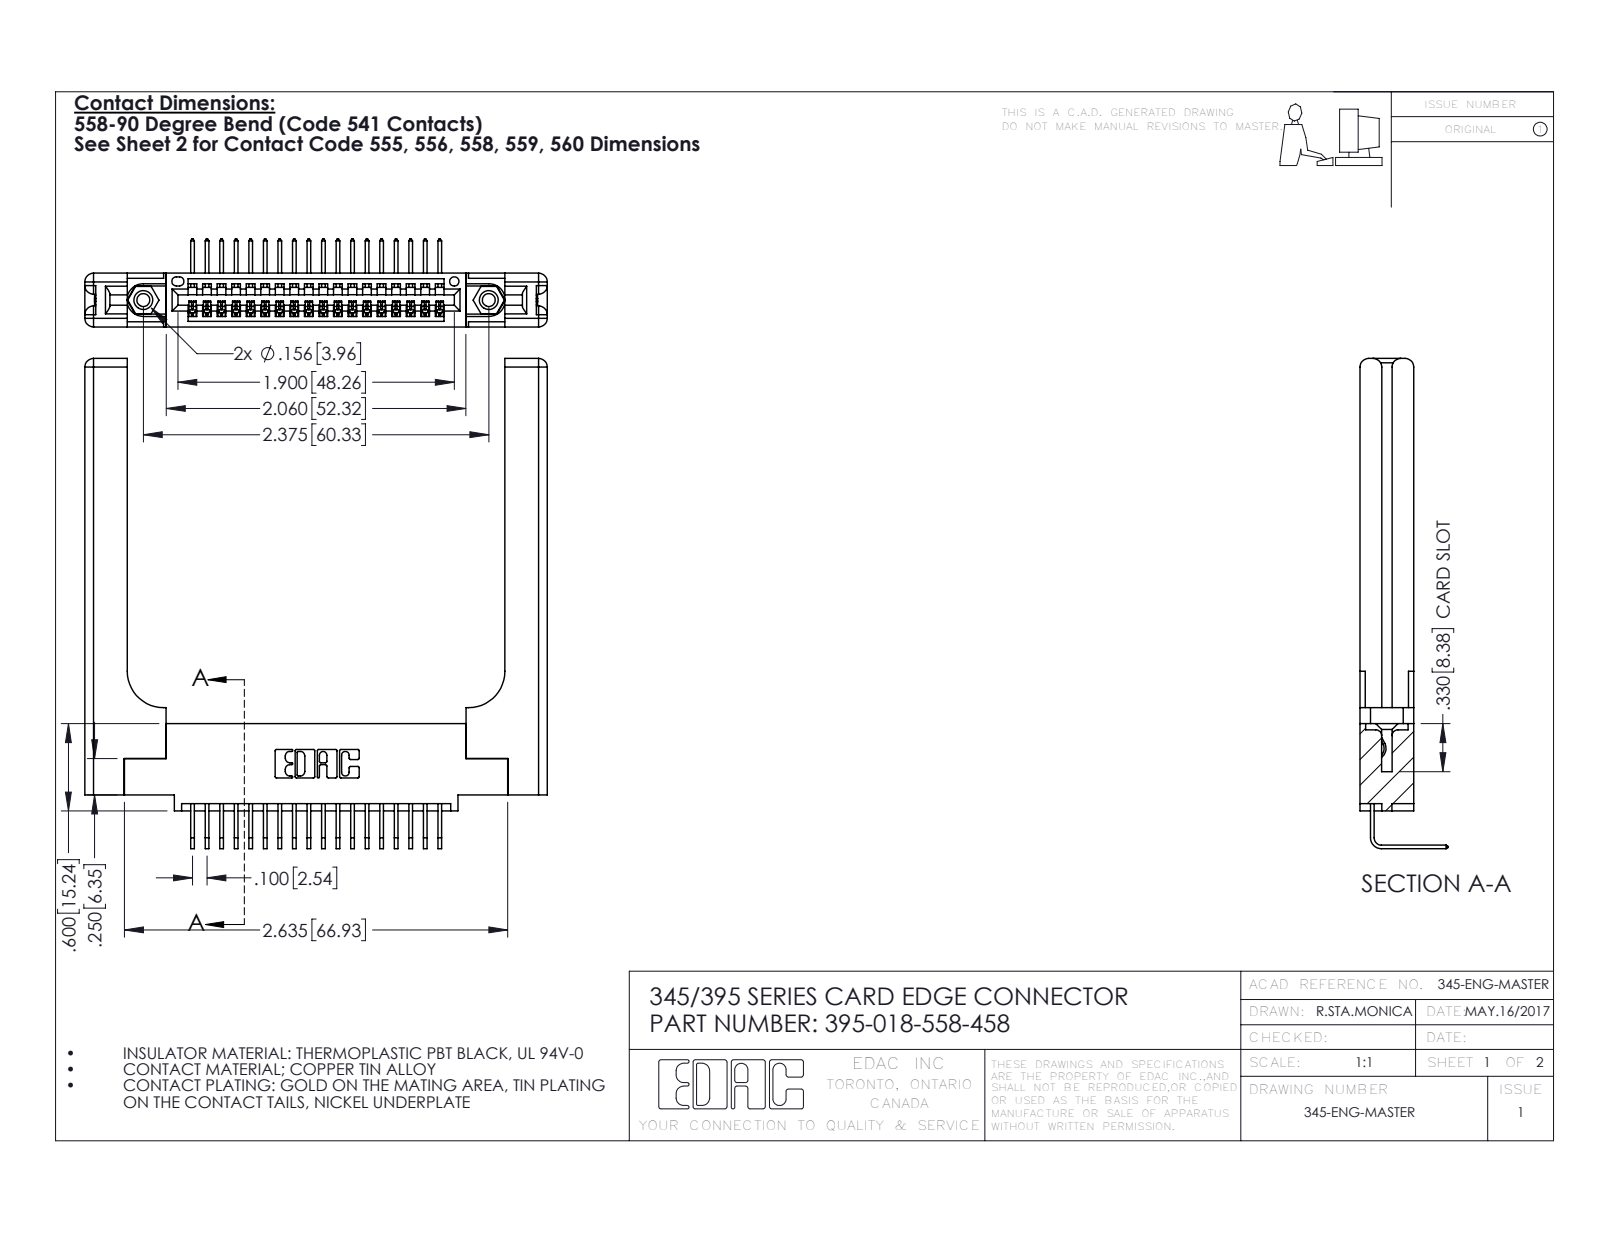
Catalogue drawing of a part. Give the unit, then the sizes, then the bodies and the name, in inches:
Units: inches
Overall size (bounding box): 3.369 × 3.179 × 0.605
Round holes (diameter × count): ⌀0.089 ×2, ⌀0.125 ×2, ⌀0.156 ×2, ⌀0.064 ×1
Round bosses / shafts (diameter × count): ⌀0.155 ×2
Partial cylindrical surfaces — rounded edges, fillets, slot ends (radius × count): R0.006 ×36, R0.01 ×22, R0.06 ×16, R0.007 ×6, R0.031 ×6, R0.026 ×3, R0.03 ×2, R0.031 ×2
Main face-to-face distances: 0.37, 0.072, 0.298, 0.148, 0.15, 0.077, 0.22, 0.098, 0.272, 0.025
Hole centre spacings: 0.27, 2.141, 2.375
Volume: 0.974 in³ · Surface area: 23.76 in²
Bodies: 23 solids, 1466 faces (988 planar, 418 cylindrical, 60 other)
Part name (STEP PRODUCT): 345-292-001_558 Tail - 2; 345-220-058_345-220-058; 345-250-001_345-250-001-102; 395-018-558-458 (+1 more)
STEP written by: SolidWorks 2016 (CONFIG_CONTROL_DESIGN)
